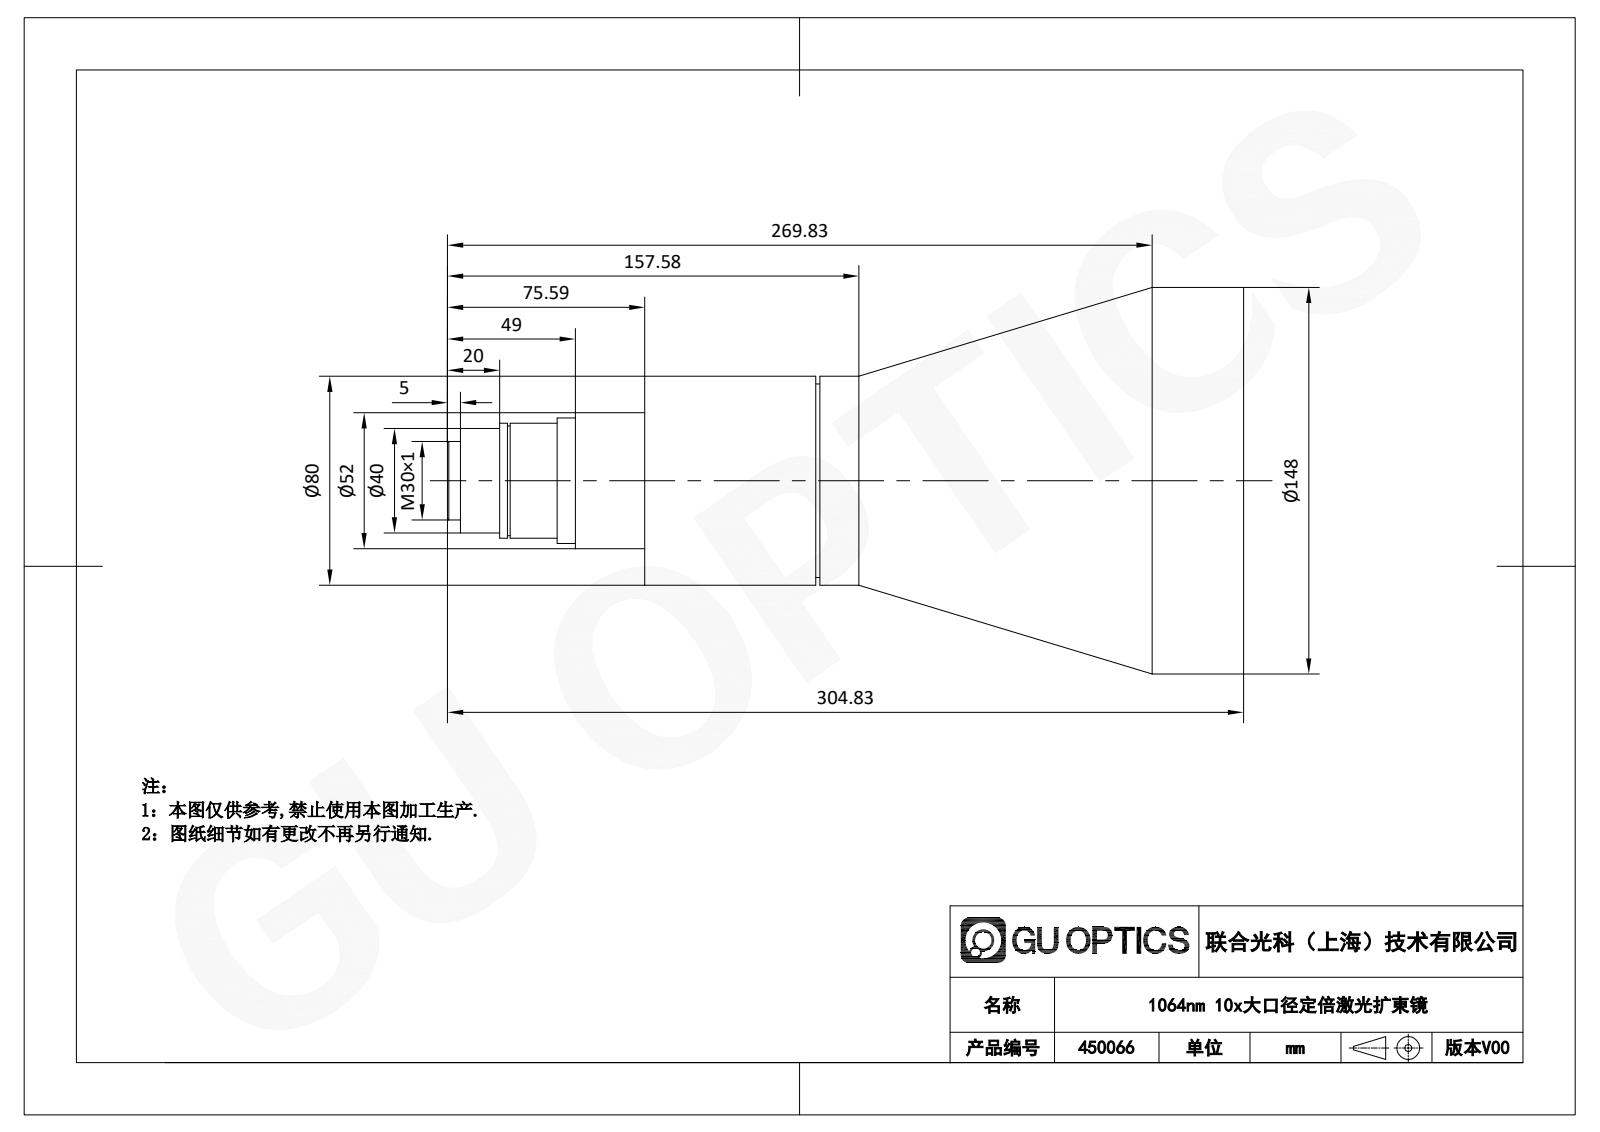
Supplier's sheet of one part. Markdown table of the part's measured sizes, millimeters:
| quantity | value |
| --- | --- |
| part name | 450066 |
| STEP written by | SolidWorks 2020 (AUTOMOTIVE_DESIGN) |
| units | millimeters |
| bodies | 1 solid, 37 faces (11 planar, 22 cylindrical, 4 other) |
| overall size | 304.83 × 148 × 148 |
| volume | 2 318 000 mm³ |
| surface area | 113 571 mm² |
| round bosses / shafts (diameter × count) | 148 × 1, 80 × 1, 74 × 1, 52 × 1, 48 × 1, 44 × 1, 42 × 1, 40 × 1 |
| main face-to-face distances | 229.24, 66.99, 162.25, 65.49, 1.5, 163.75, 75.59, 141.08, 142.58, 304.83 |
